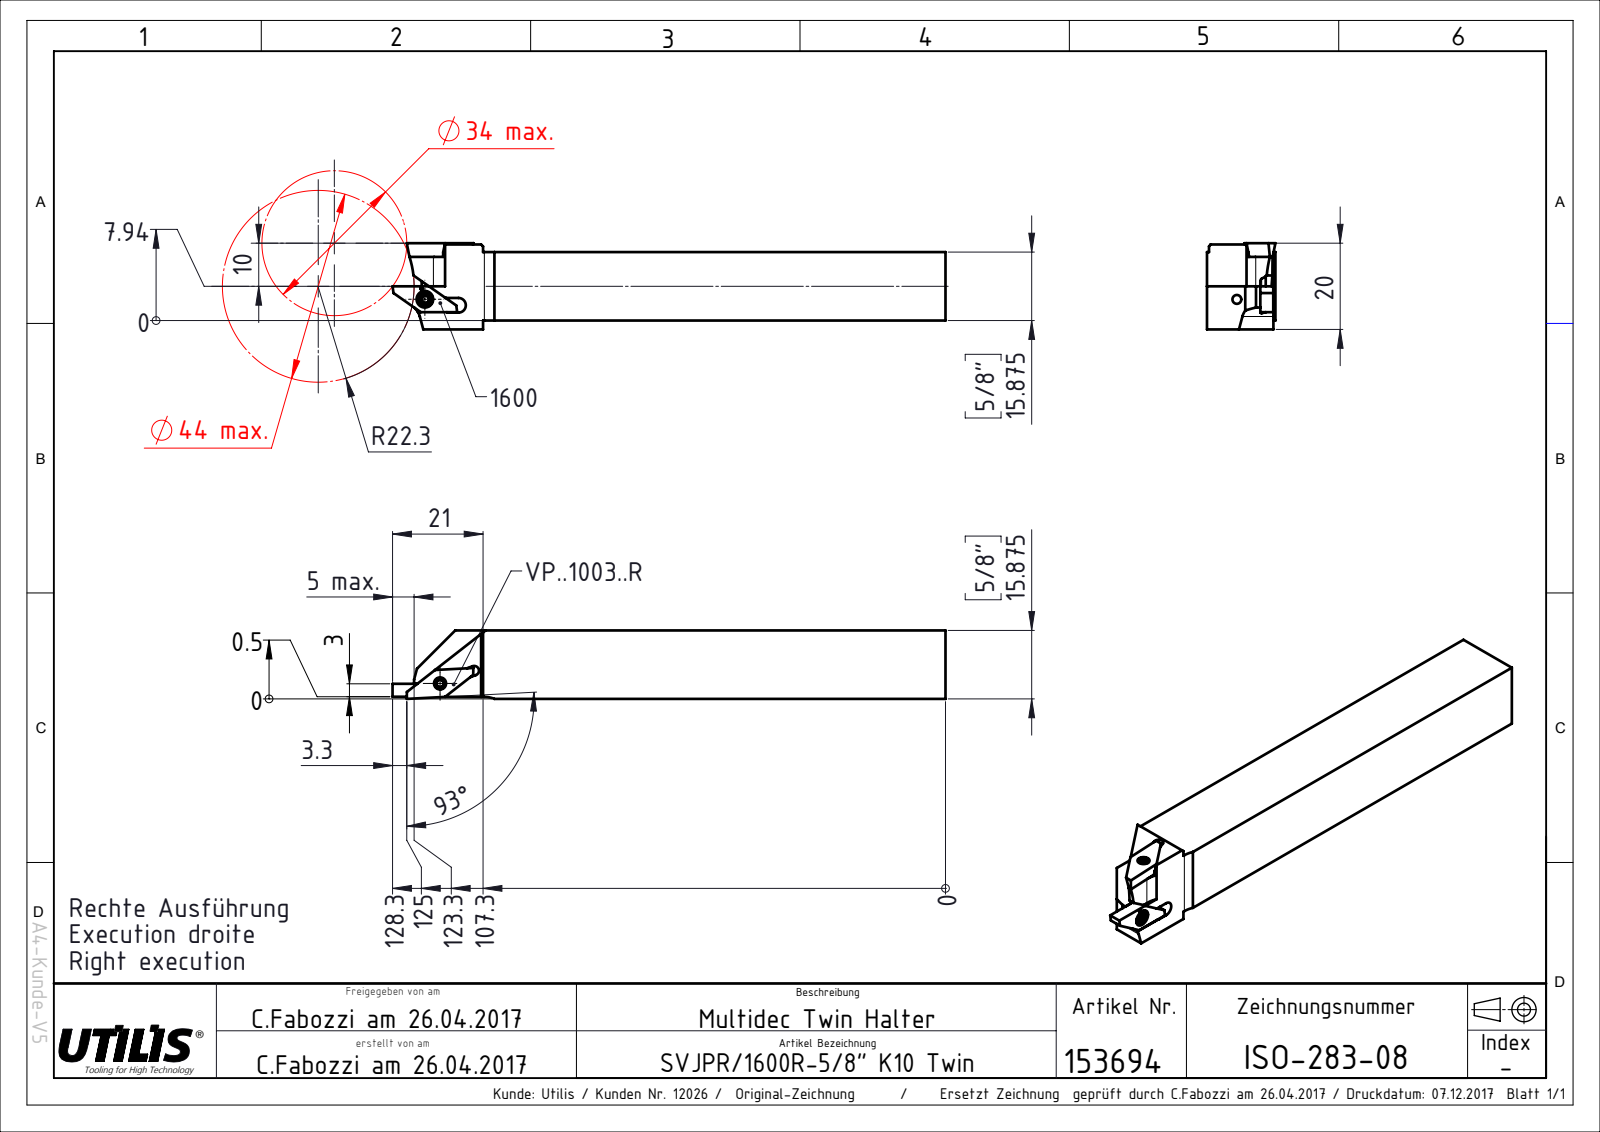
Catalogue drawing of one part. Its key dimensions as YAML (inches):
part_name: "ISO-283-08"
step_written_by: "SolidWorks 2016 (AUTOMOTIVE_DESIGN)"
units: inches
bodies: {solids: 1, faces: 82, planar: 67, cylindrical: 13, other: 2}
overall_size: [5.051, 0.787, 0.625]
volume: 1.85
surface_area: 13.25
partial_cylinders:
  - {radius: 0.24, count: 3}
  - {radius: 0.01, count: 2}
  - {radius: 0.02, count: 1}
  - {radius: 0.043, count: 1}
  - {radius: 0.061, count: 1}
  - {radius: 0.067, count: 1}
  - {radius: 0.161, count: 1}
  - {radius: 0.878, count: 1}
face_to_face_distances: [0.625, 0.081, 0.706, 0.607, 0.019, 0.313, 0.394, 0.776, 0.694, 0.382]
